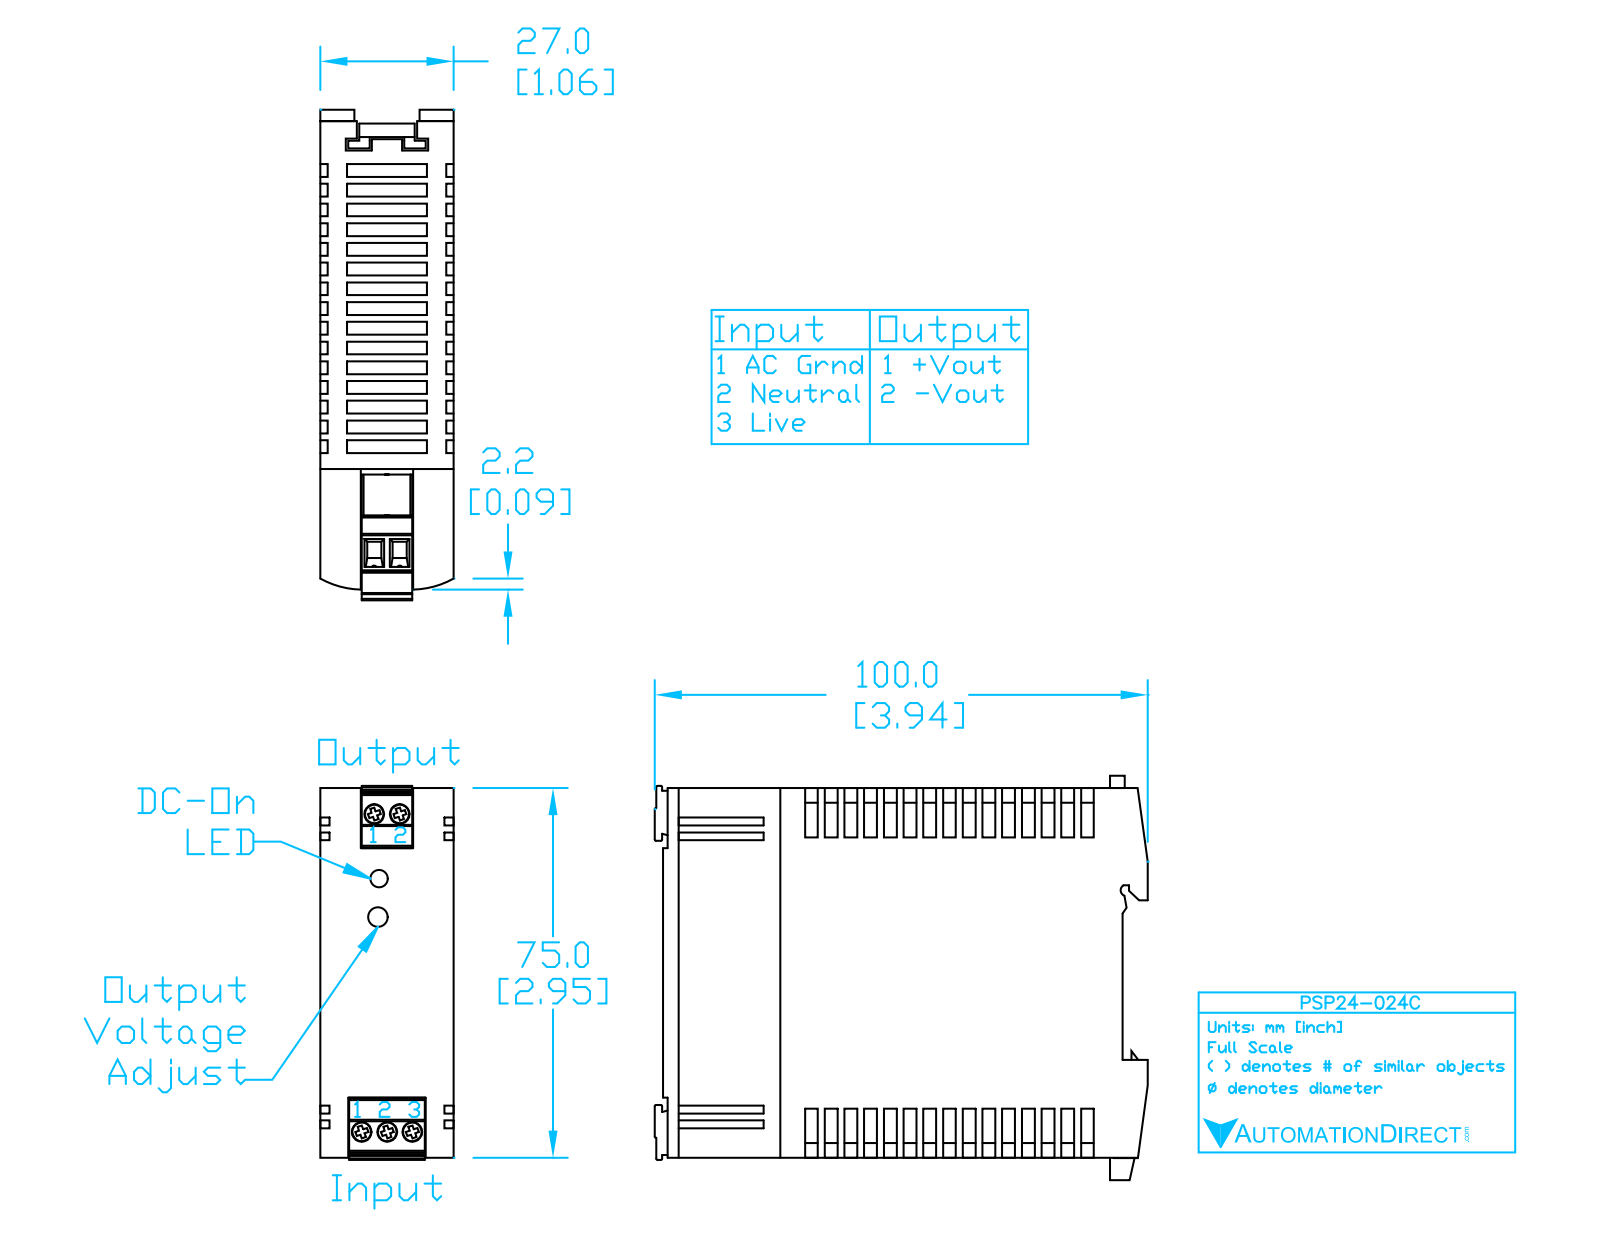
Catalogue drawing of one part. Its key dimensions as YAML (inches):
part_name: "PSP24-024C"
step_written_by: "SolidWorks 2011 (CONFIG_CONTROL_DESIGN)"
units: inches
bodies: {solids: 11, faces: 341, planar: 290, cylindrical: 0, other: 51}
overall_size: [3.955, 3.15, 1.063]
volume: 11.75
surface_area: 52.23
face_to_face_distances: [1.063, 2.953, 0.079, 0.207, 0.856, 0.63, 0.549, 0.492, 2.461, 2.789]
